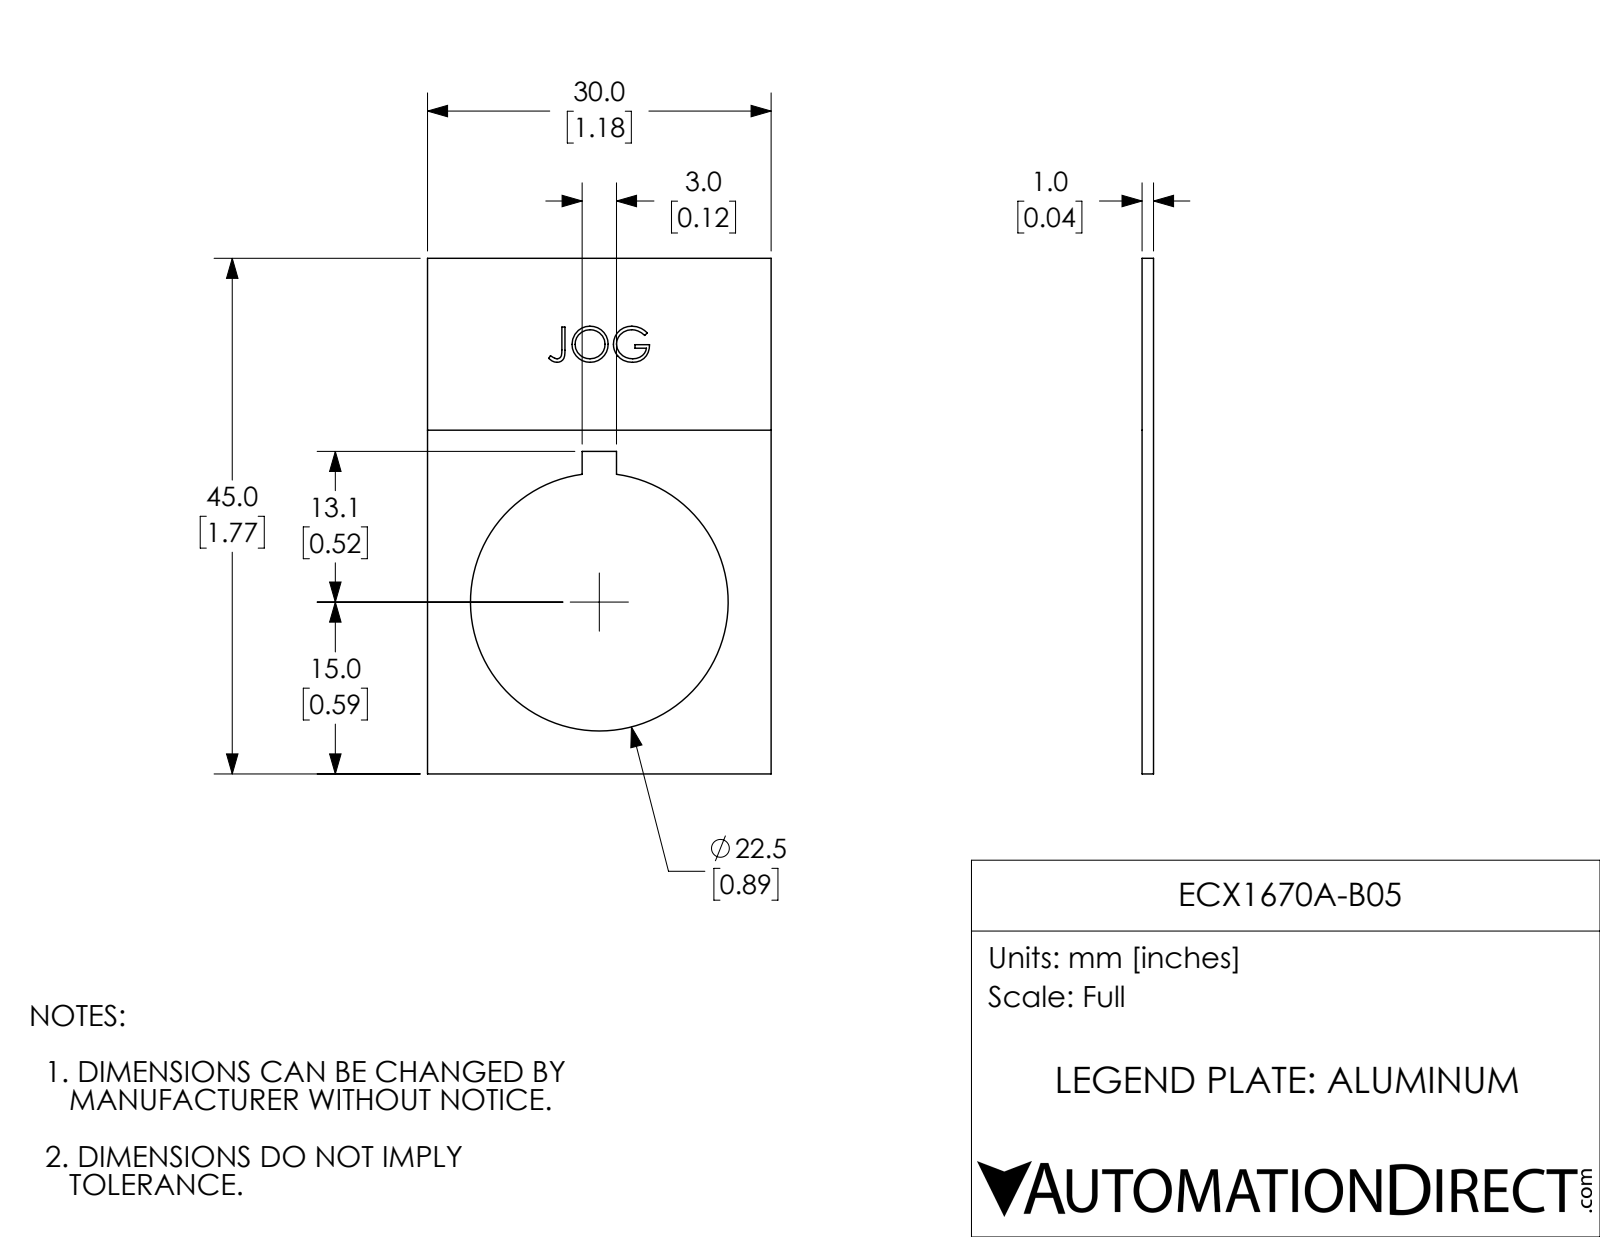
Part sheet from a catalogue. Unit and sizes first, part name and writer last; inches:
Units: inches
Overall size (bounding box): 1.772 × 1.181 × 0.039
Round holes (diameter × count): ⌀0.886 ×1
Main face-to-face distances: 0.039, 1.181, 1.772, 0.038, 0.531, 0.65, 1.108, 0.663, 0.118, 0.472
Volume: 0.058 in³ · Surface area: 3.285 in²
Bodies: 1 solid, 47 faces (22 planar, 3 cylindrical, 22 other)
Part name (STEP PRODUCT): ECX1670A-B05
STEP written by: SolidWorks 2017 (AUTOMOTIVE_DESIGN)
